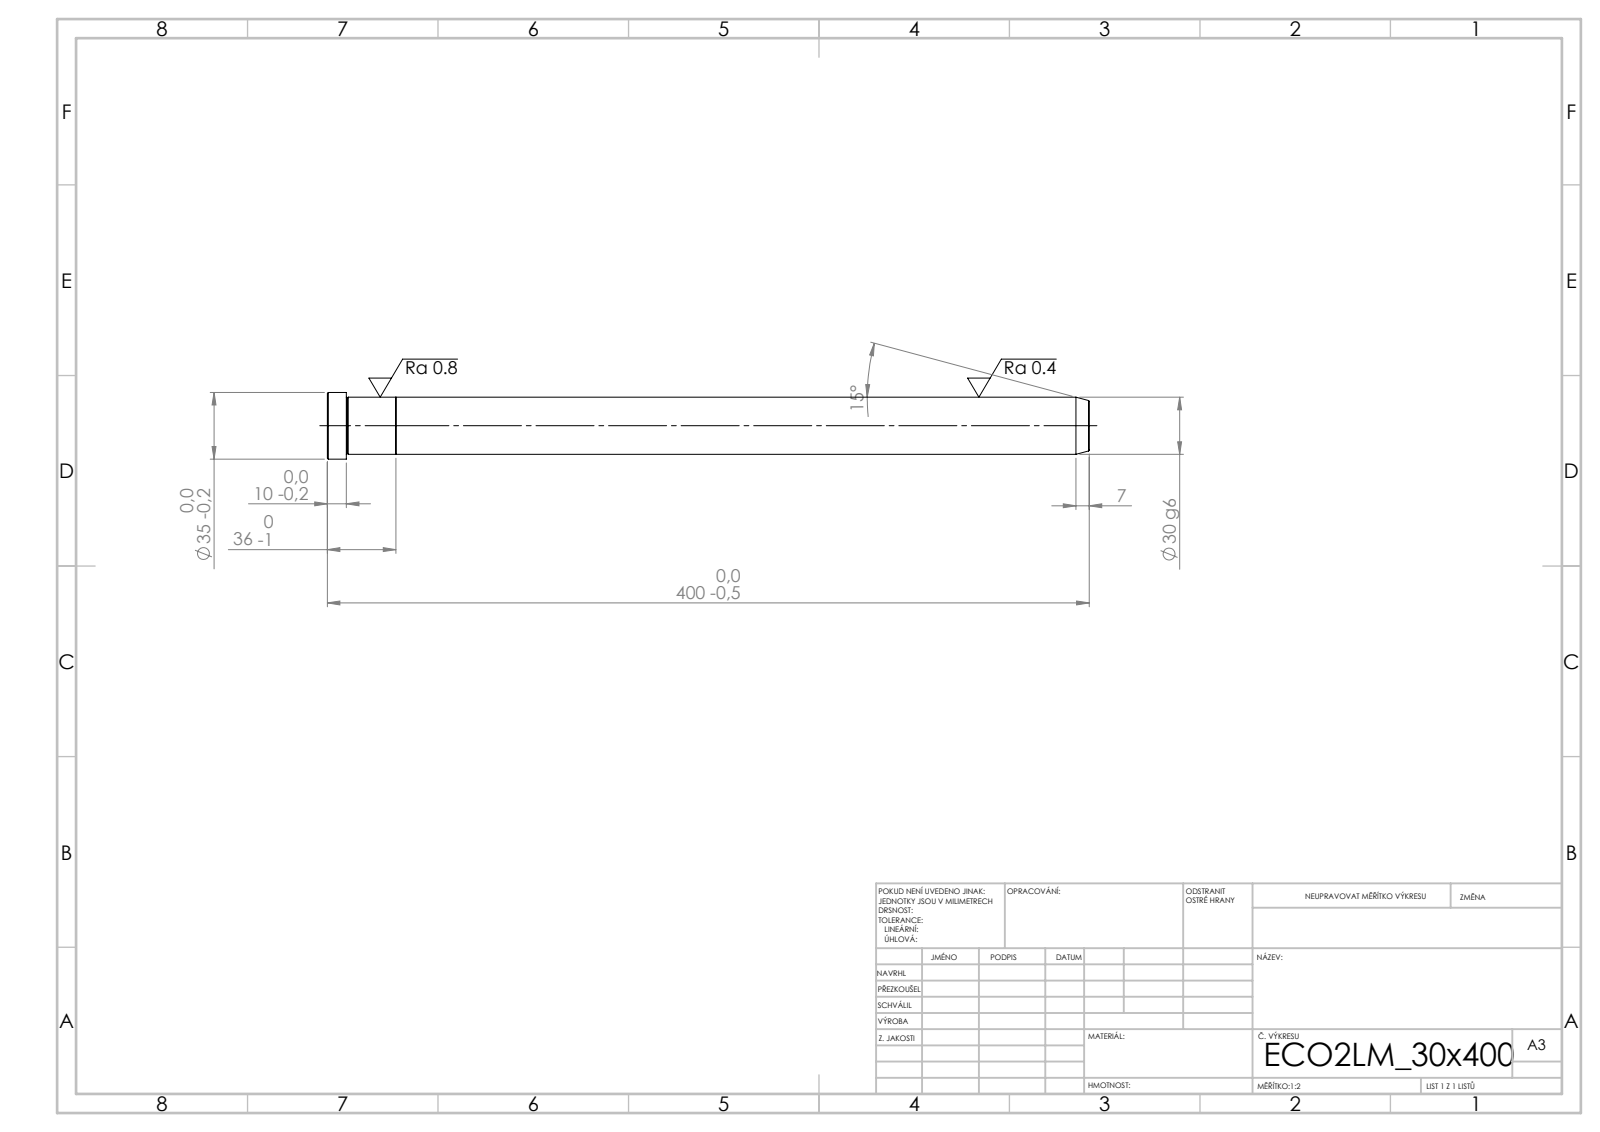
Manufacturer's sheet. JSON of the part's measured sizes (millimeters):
{"step_written_by": "SolidWorks 2019 (CONFIG_CONTROL_DESIGN)", "units": "millimeters", "bodies": {"solids": 2, "faces": 21, "planar": 5, "cylindrical": 6, "other": 10}, "overall_size": [400, 35, 35], "volume_mm3": 284651, "surface_area_mm2": 41018, "round_bosses_or_shafts": [[35, 1], [30, 1]], "face_to_face_distances": [36, 364, 400, 390, 26, 10]}
